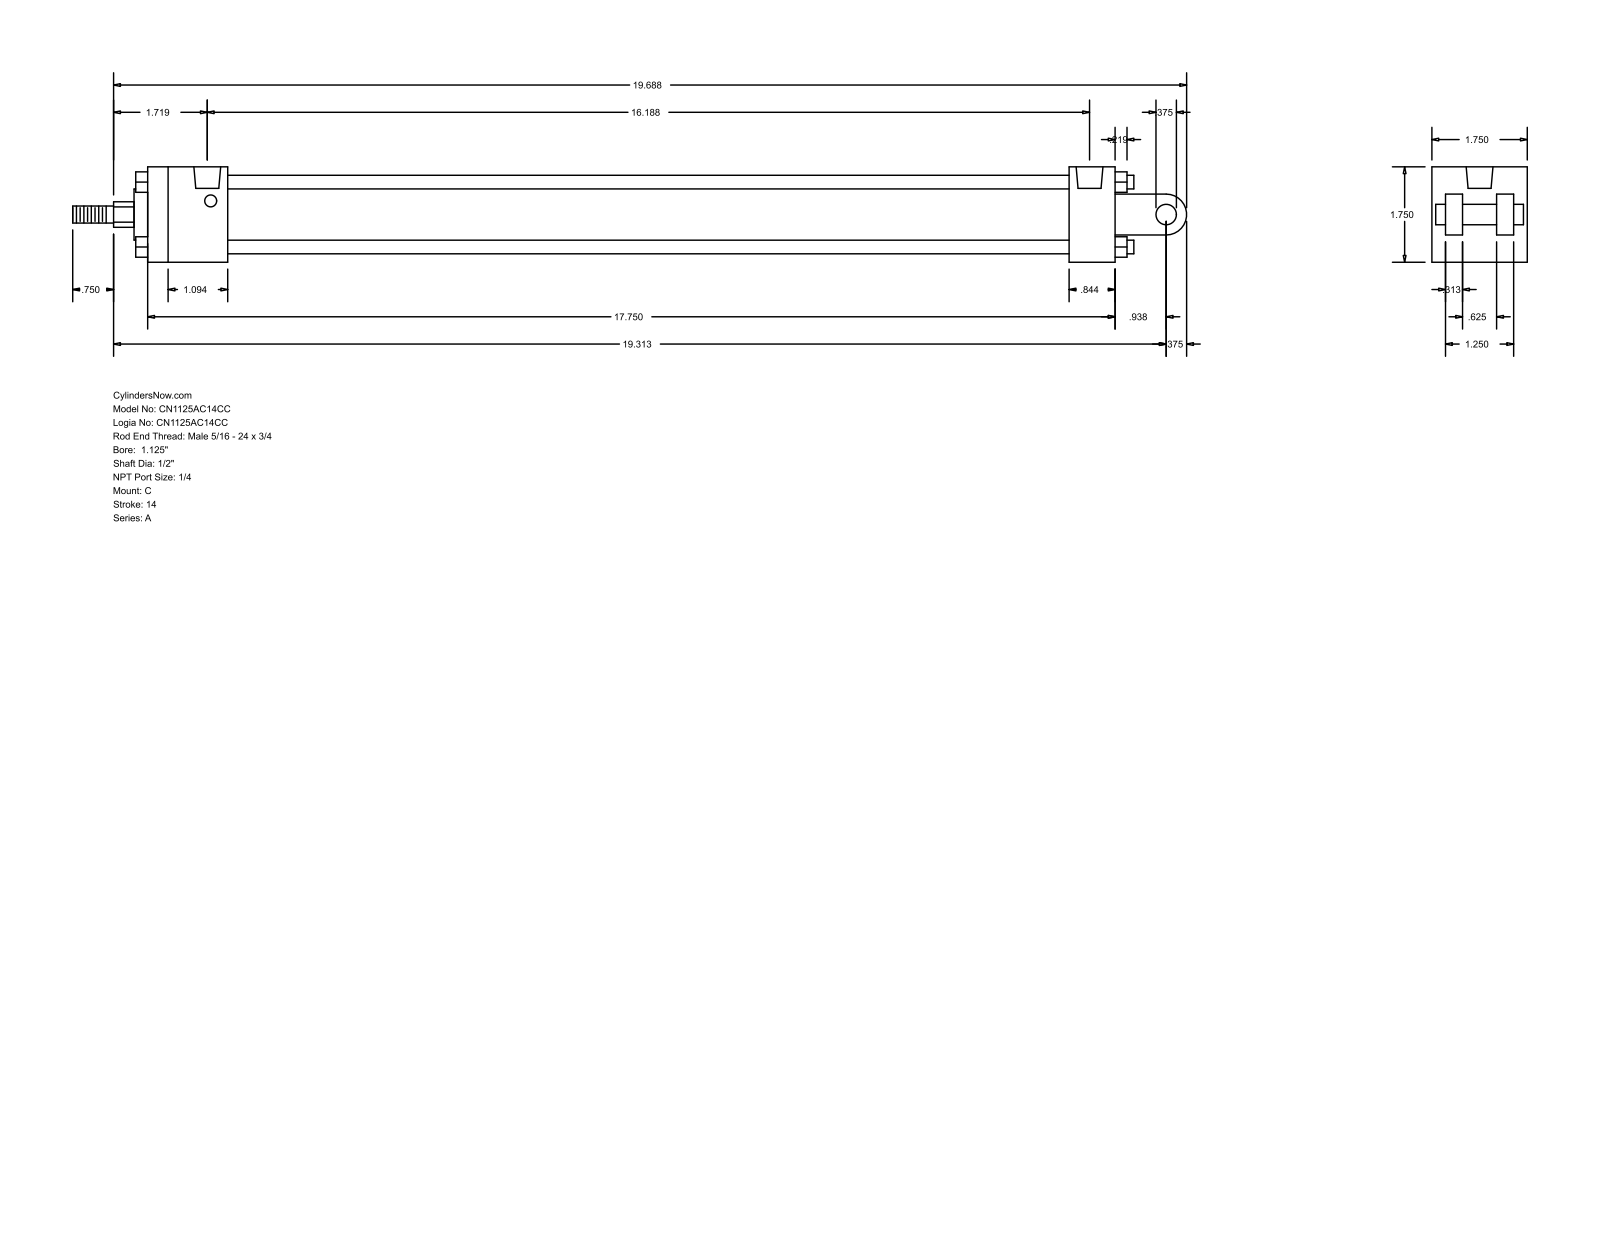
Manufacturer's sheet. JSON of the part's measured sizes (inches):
{"part_name": "A_C__0112_0.5", "step_written_by": "GSSL Pune (CONFIG_CONTROL_DESIGN)", "units": "inches", "bodies": {"solids": 0, "faces": 135, "planar": 102, "cylindrical": 33, "other": 0}, "overall_size": [20.437, 1.75, 1.75], "round_holes": [[0.219, 4], [0.492, 2]], "round_bosses_or_shafts": [[0.25, 4], [1.255, 1], [0.937, 1], [0.5, 1], [0.375, 1], [0.313, 1]], "partial_cylinders_radius": [[0.234, 1], [0.375, 1]], "face_to_face_distances": [1.75, 0.25, 1.25, 0.563, 17.75, 1.188, 16.906, 0.844, 1.469, 15.437], "hole_center_spacings": [16.063, 0.062, 0.063, 16.125, 16.125, 16.187]}
